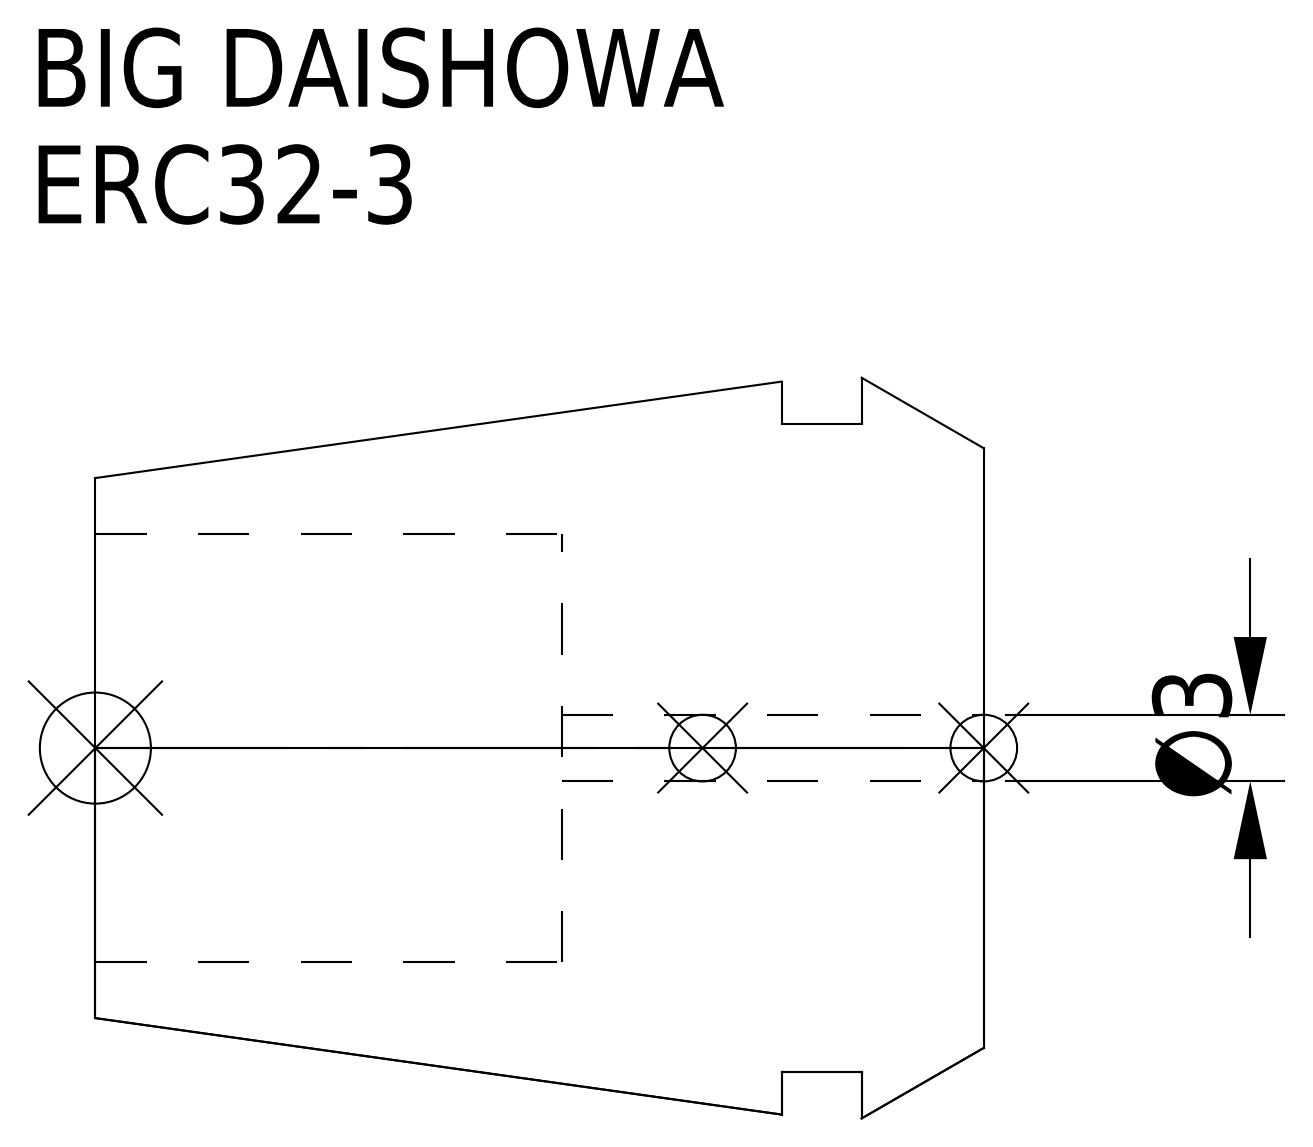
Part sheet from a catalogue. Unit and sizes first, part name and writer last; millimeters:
Units: millimetres
Overall size (bounding box): 40 × 33.35 × 33.35
Round holes (diameter × count): ⌀3 ×1, ⌀19.3 ×1
Round bosses / shafts (diameter × count): ⌀29.2 ×1
Main face-to-face distances: 19, 5.5, 13.5, 9.1, 3.6, 9.9, 40, 34.5, 30.9, 21
Volume: 20 164 mm³ · Surface area: 6 606 mm²
Bodies: 1 solid, 15 faces (5 planar, 6 cylindrical, 4 other)
Part name (STEP PRODUCT): ERC32-3
STEP written by: CREO PARAMETRIC BY PTC INC, 2016380 (AUTOMOTIVE_DESIGN)
